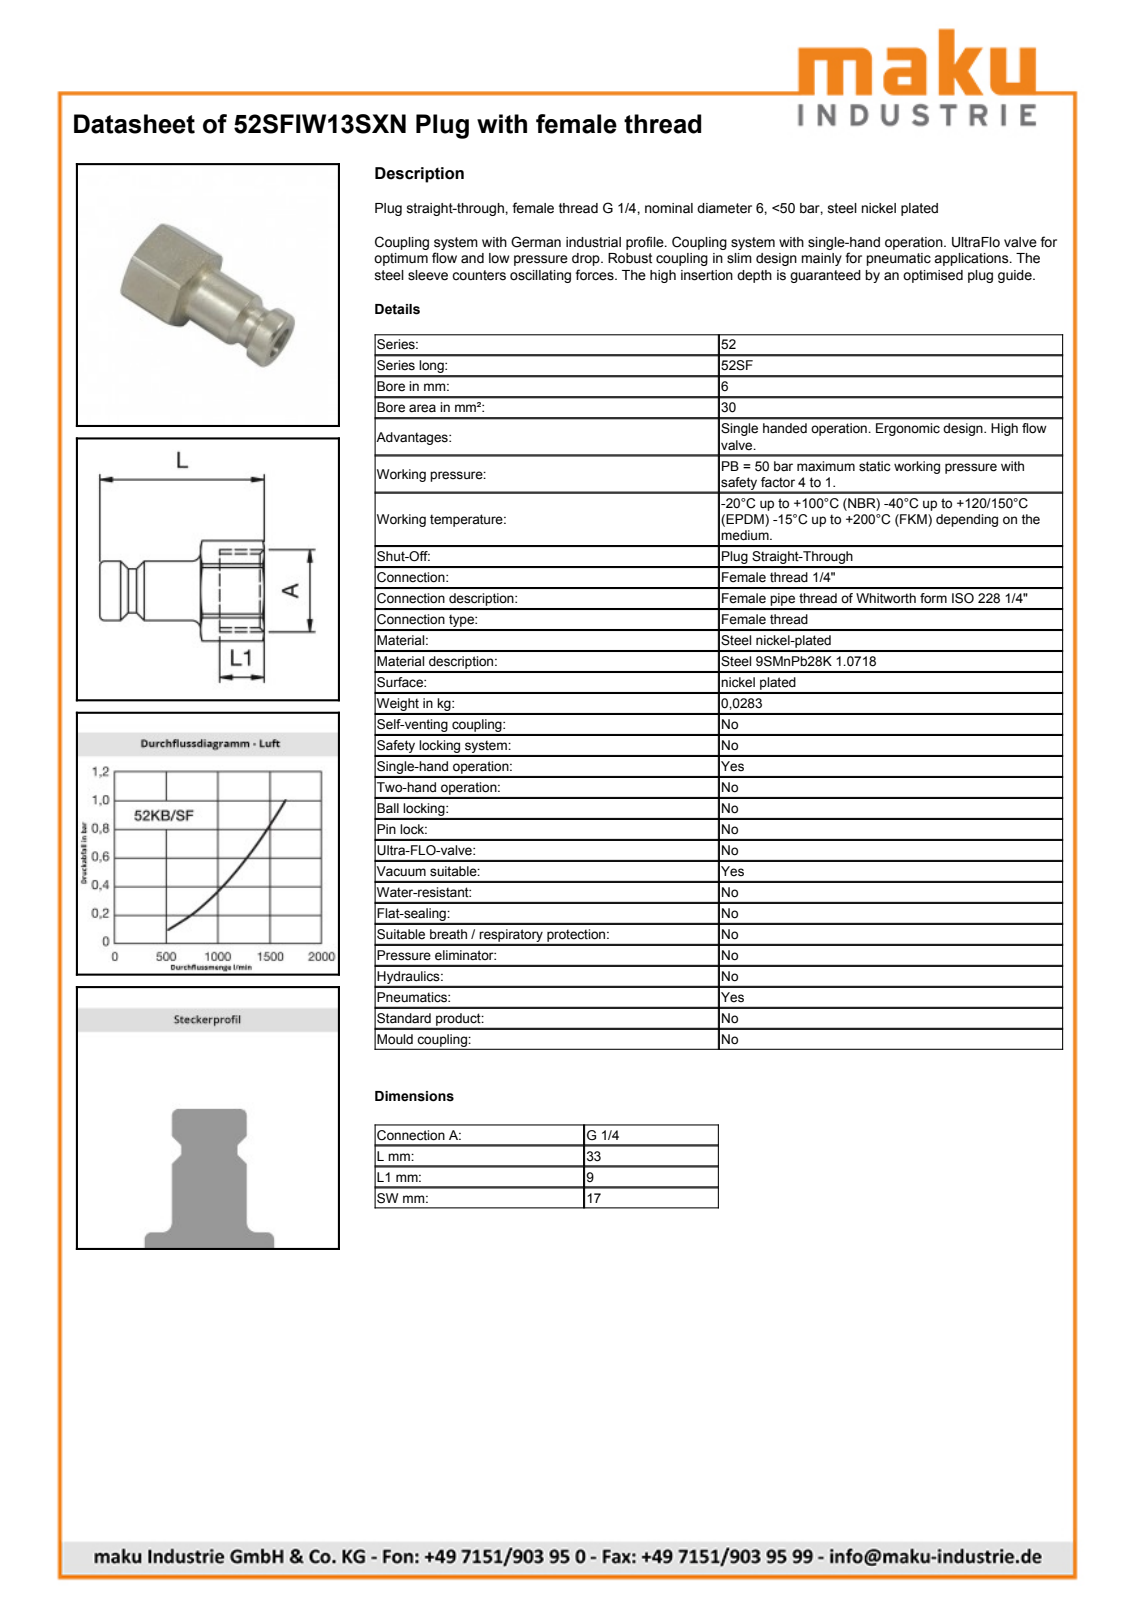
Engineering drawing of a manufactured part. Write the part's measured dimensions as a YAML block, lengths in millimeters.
part_name: "D105388"
step_written_by: "Autodesk Inventor 2011 (AUTOMOTIVE_DESIGN)"
units: millimeters
bodies: {solids: 1, faces: 38, planar: 10, cylindrical: 11, other: 17}
overall_size: [33.25, 19.15, 17]
volume: 3603
surface_area: 2702
round_holes:
  - {diameter: 6.5, count: 1}
  - {diameter: 11.45, count: 1}
round_bosses_or_shafts:
  - {diameter: 11.95, count: 1}
  - {diameter: 8.9, count: 1}
partial_cylinders:
  - {radius: 9.57, count: 1}
face_to_face_distances: [17, 9, 24.25, 33.25, 20.4, 3.85, 12.85]
